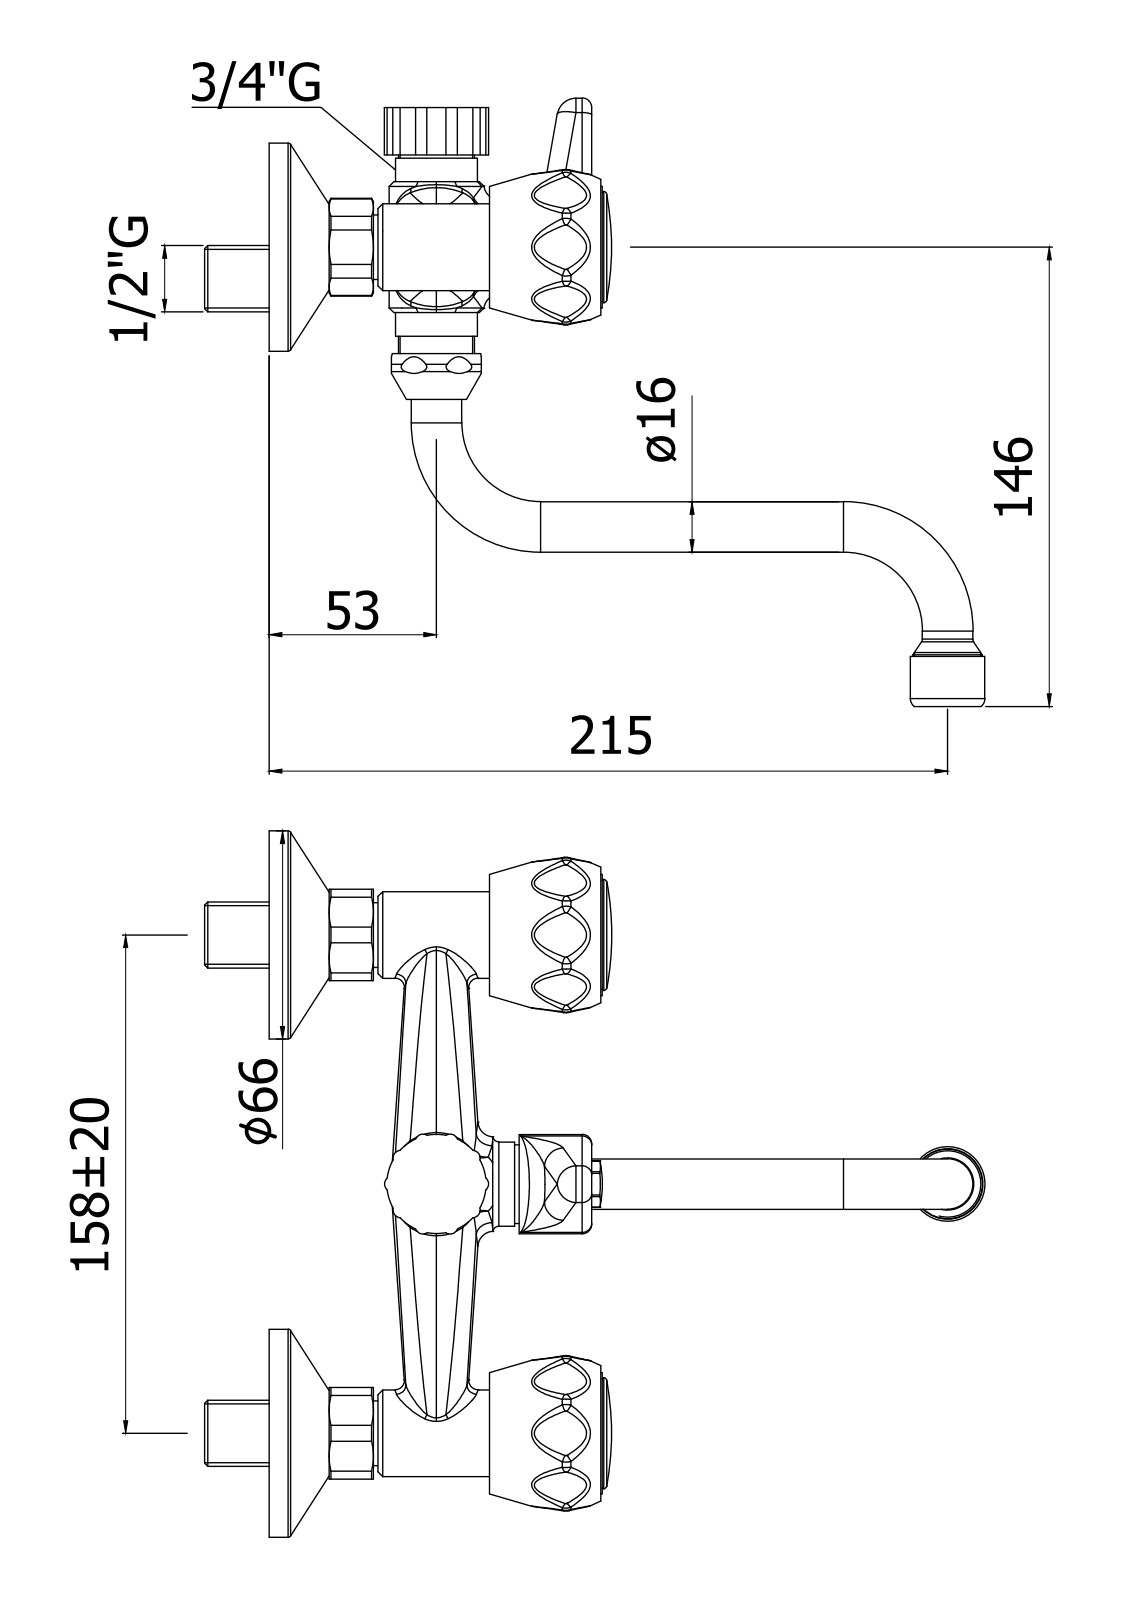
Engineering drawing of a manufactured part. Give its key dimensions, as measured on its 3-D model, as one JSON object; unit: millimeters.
{"part_name": "DA169CR", "step_written_by": "CREO PARAMETRIC BY PTC INC, 2020044 (CONFIG_CONTROL_DESIGN)", "units": "millimeters", "bodies": {"solids": 4, "faces": 814, "planar": 94, "cylindrical": 167, "other": 553}, "overall_size": [226.8, 224, 192.9], "volume_mm3": 393064, "surface_area_mm2": 101028, "round_holes": [[17, 3], [19, 2], [21.5, 2], [11.6, 1], [12.4, 1], [14.6, 1], [15.2, 1], [16.5, 1], [17.2, 1], [20, 1], [20.5, 1], [22.6, 1]], "round_bosses_or_shafts": [[16, 3], [66, 2], [38.5, 2], [27.5, 2], [22, 2], [31.5, 1], [26.7, 1], [26, 1]], "partial_cylinders_radius": [[21.31, 16], [2.5, 10], [6, 3], [15.5, 3], [3, 2], [10.25, 2], [15, 2], [7.35, 1]], "face_to_face_distances": [69.8, 33, 36.8, 29, 23, 35.3, 102.2, 69.2, 32.4, 79.2], "hole_center_spacings": [79, 158]}
